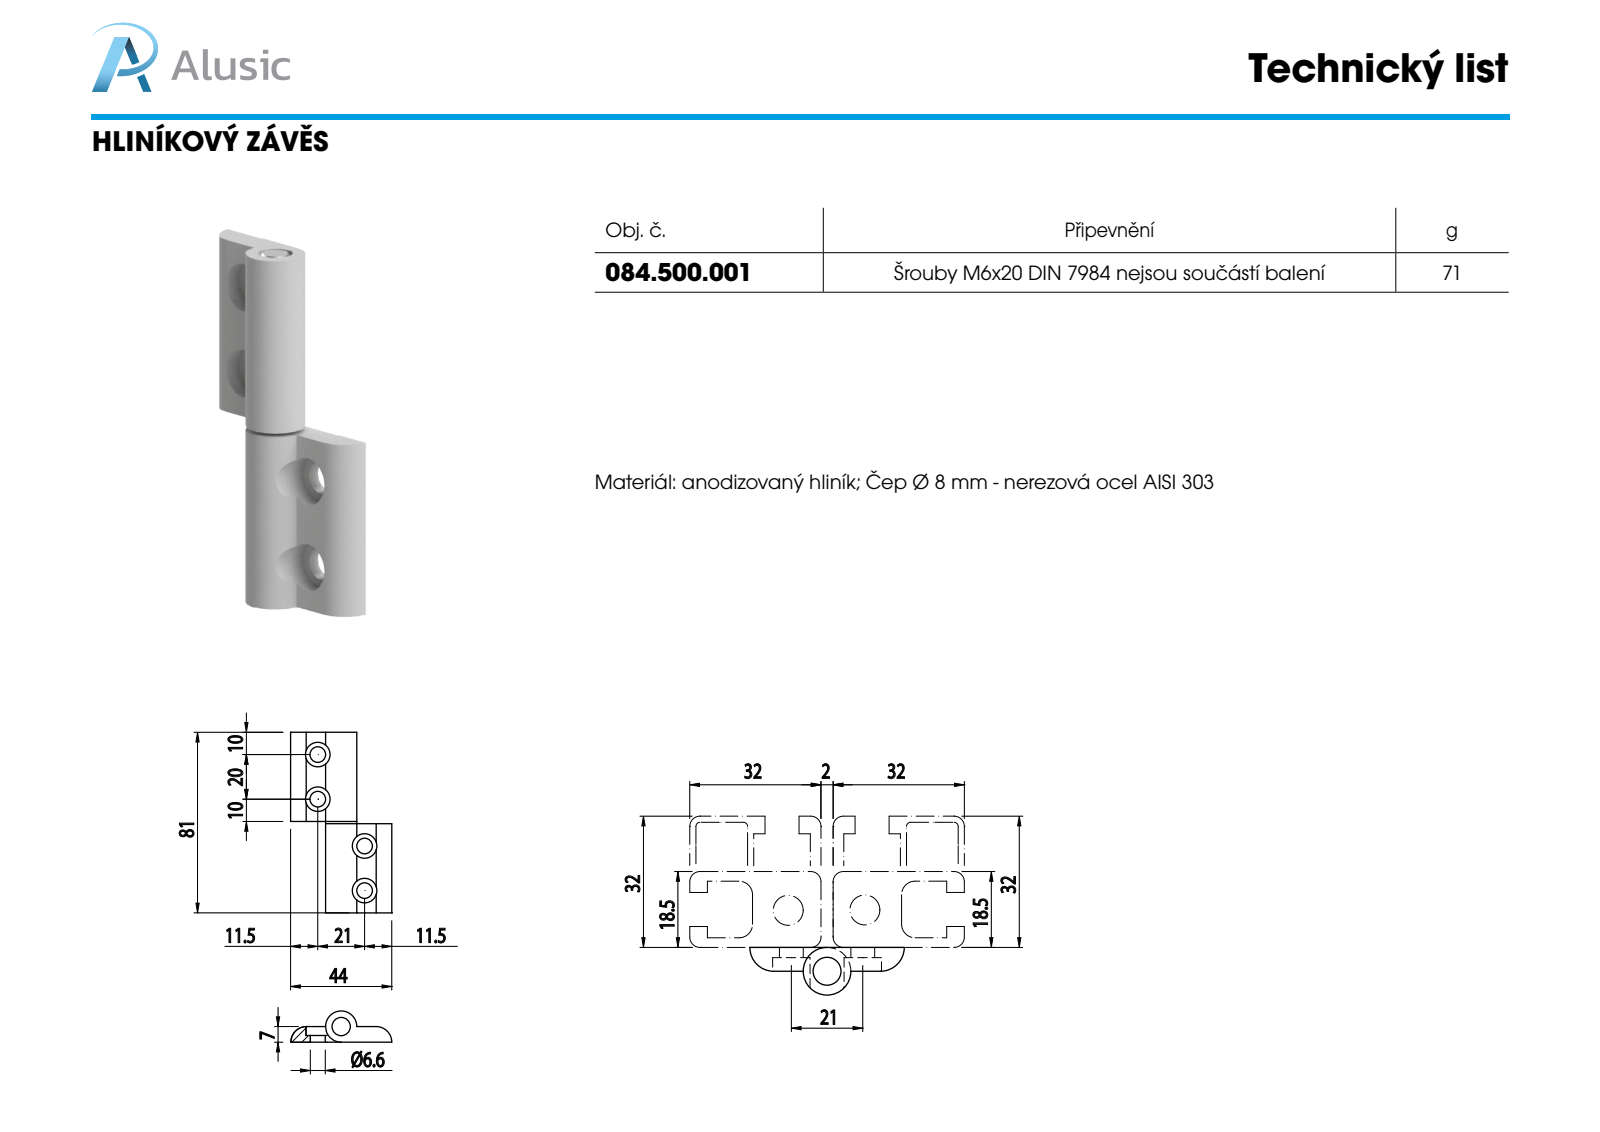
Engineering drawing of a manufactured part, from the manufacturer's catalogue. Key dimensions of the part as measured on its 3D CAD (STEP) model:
Part name (STEP PRODUCT): PERNO CERNIERA_084.500.001.B; SEMI CERNIERA_084.500.001.A; 084.500.001
STEP written by: SolidWorks 2011 (CONFIG_CONTROL_DESIGN)
Units: millimetres
Bodies: 3 solids, 170 faces (138 planar, 28 cylindrical, 4 other)
Overall size (bounding box): 81 × 45.66 × 14
Volume: 18 642 mm³ · Surface area: 11 614 mm²
Round holes (diameter × count): ⌀6.6 ×4, ⌀11 ×4, ⌀8.2 ×1
Round bosses / shafts (diameter × count): ⌀14 ×1, ⌀8 ×1
Partial cylindrical surfaces — rounded edges, fillets, slot ends (radius × count): R6.7 ×2
Main face-to-face distances: 40, 6.7, 3, 3.7, 80, 6.11, 1, 41, 81, 6.12
Hole centre spacings: 20
